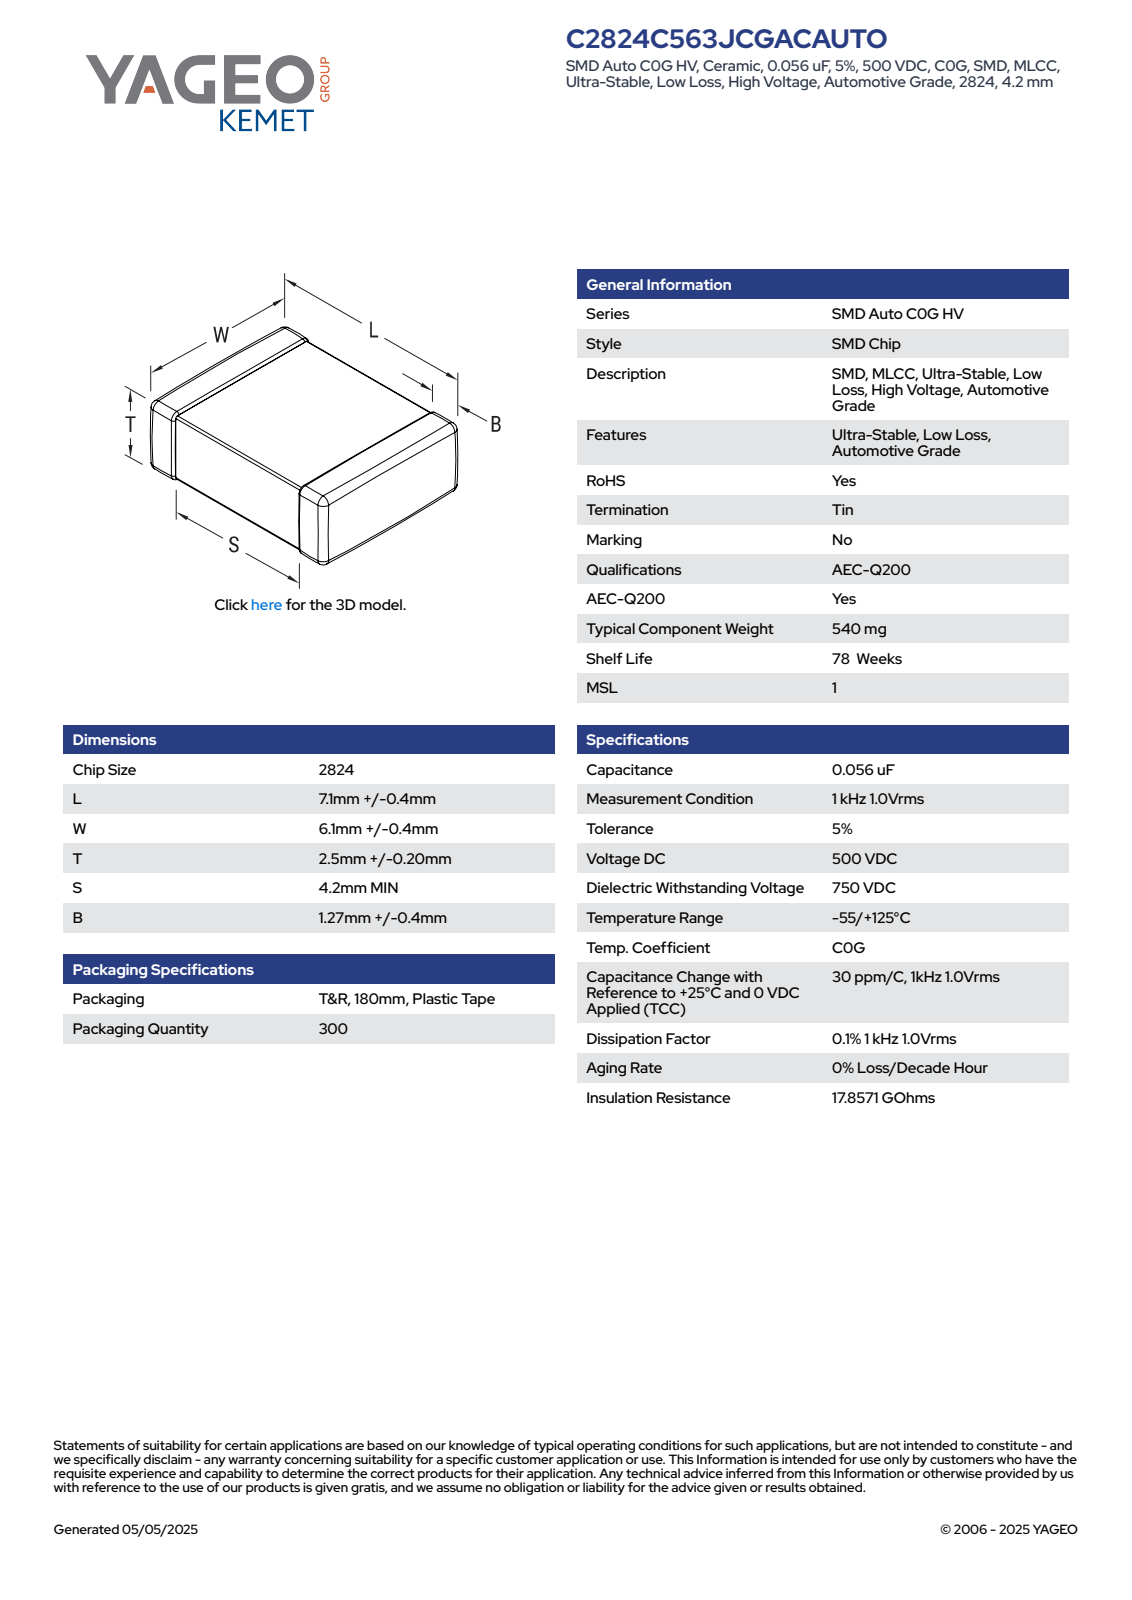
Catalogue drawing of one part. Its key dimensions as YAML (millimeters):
part_name: "CCS_CCSTD_2824_L7.5W6.5T2.7B1.27"
step_written_by: "SolidWorks 2021 (AUTOMOTIVE_DESIGN)"
units: millimeters
bodies: {solids: 4, faces: 125, planar: 71, cylindrical: 38, other: 16}
overall_size: [7.5, 6.5, 2.7]
volume: 121
surface_area: 173
partial_cylinders:
  - {radius: 0.14, count: 24}
face_to_face_distances: [2.56, 2.42, 2.7, 7.5, 6.36, 6.22, 6.5, 2.57, 2.43, 3.45]
